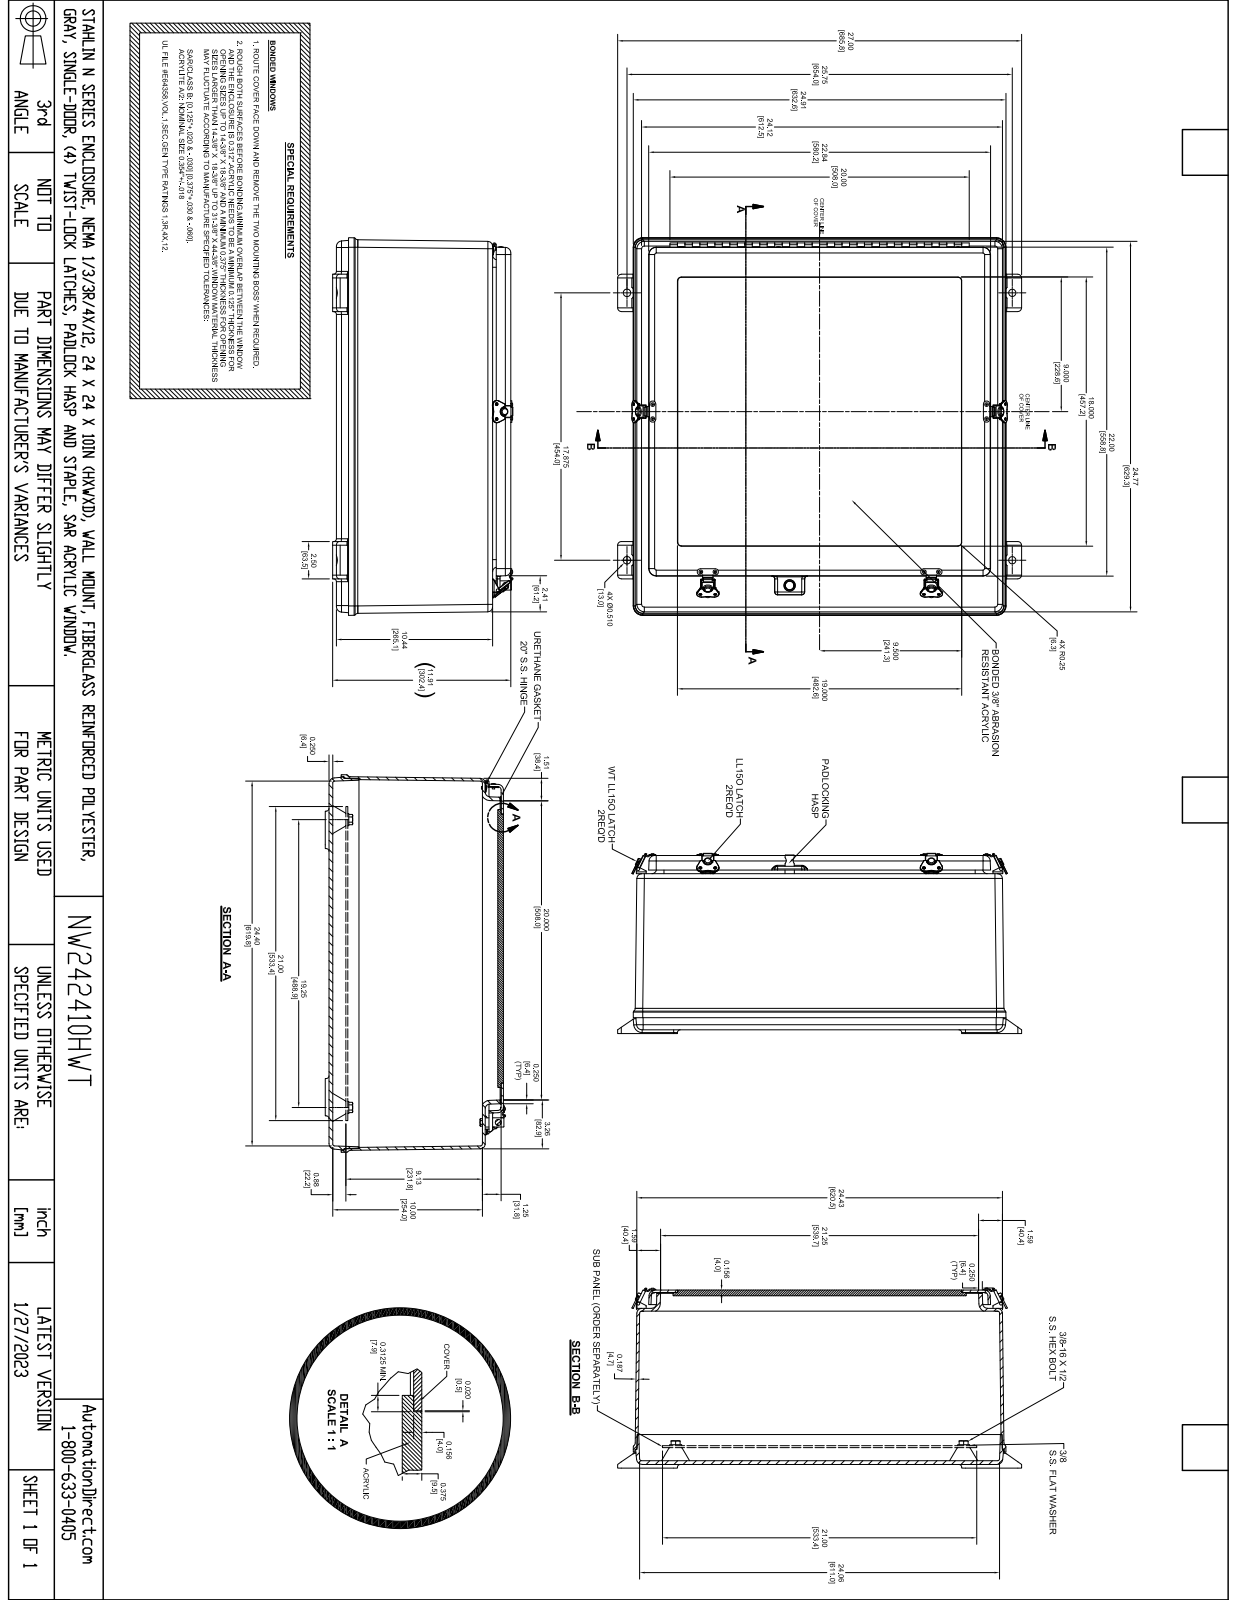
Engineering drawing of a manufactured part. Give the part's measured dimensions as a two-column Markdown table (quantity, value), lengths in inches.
| quantity | value |
| --- | --- |
| part name | TW242410HWT |
| STEP written by | SolidWorks 2018 (AUTOMOTIVE_DESIGN) |
| units | inches |
| bodies | 59 solids, 1597 faces (606 planar, 614 cylindrical, 377 other) |
| overall size | 27 × 25.25 × 12.056 |
| volume | 584 in³ |
| surface area | 5 427 in² |
| round holes (diameter × count) | 0.13 × 32, 0.063 × 16, 0.138 × 8, 0.187 × 8, 0.065 × 7, 0.307 × 4, 0.563 × 4, 0.135 × 3, 0.156 × 3, 0.5 × 2, 0.51 × 2, 0.065 × 1 |
| round bosses / shafts (diameter × count) | 0.14 × 16, 0.297 × 8, 0.5 × 4, 0.2 × 3, 0.25 × 1, 0.201 × 1, 0.135 × 1 |
| partial cylindrical surfaces (radius × count) | 0.01 × 101, 0.25 × 28, 0.187 × 18, 0.03 × 16, 0.312 × 16, 0.375 × 12, 0.5 × 12, 0.125 × 10 |
| main face-to-face distances | 0.187, 0.25, 11.659, 11.409, 11.284, 11.034, 0.375, 0.156, 0.219, 11.503 |
| hole center spacings | 6.5, 12, 23.032, 0.751, 0.937, 1, 1.512, 3.322 |
